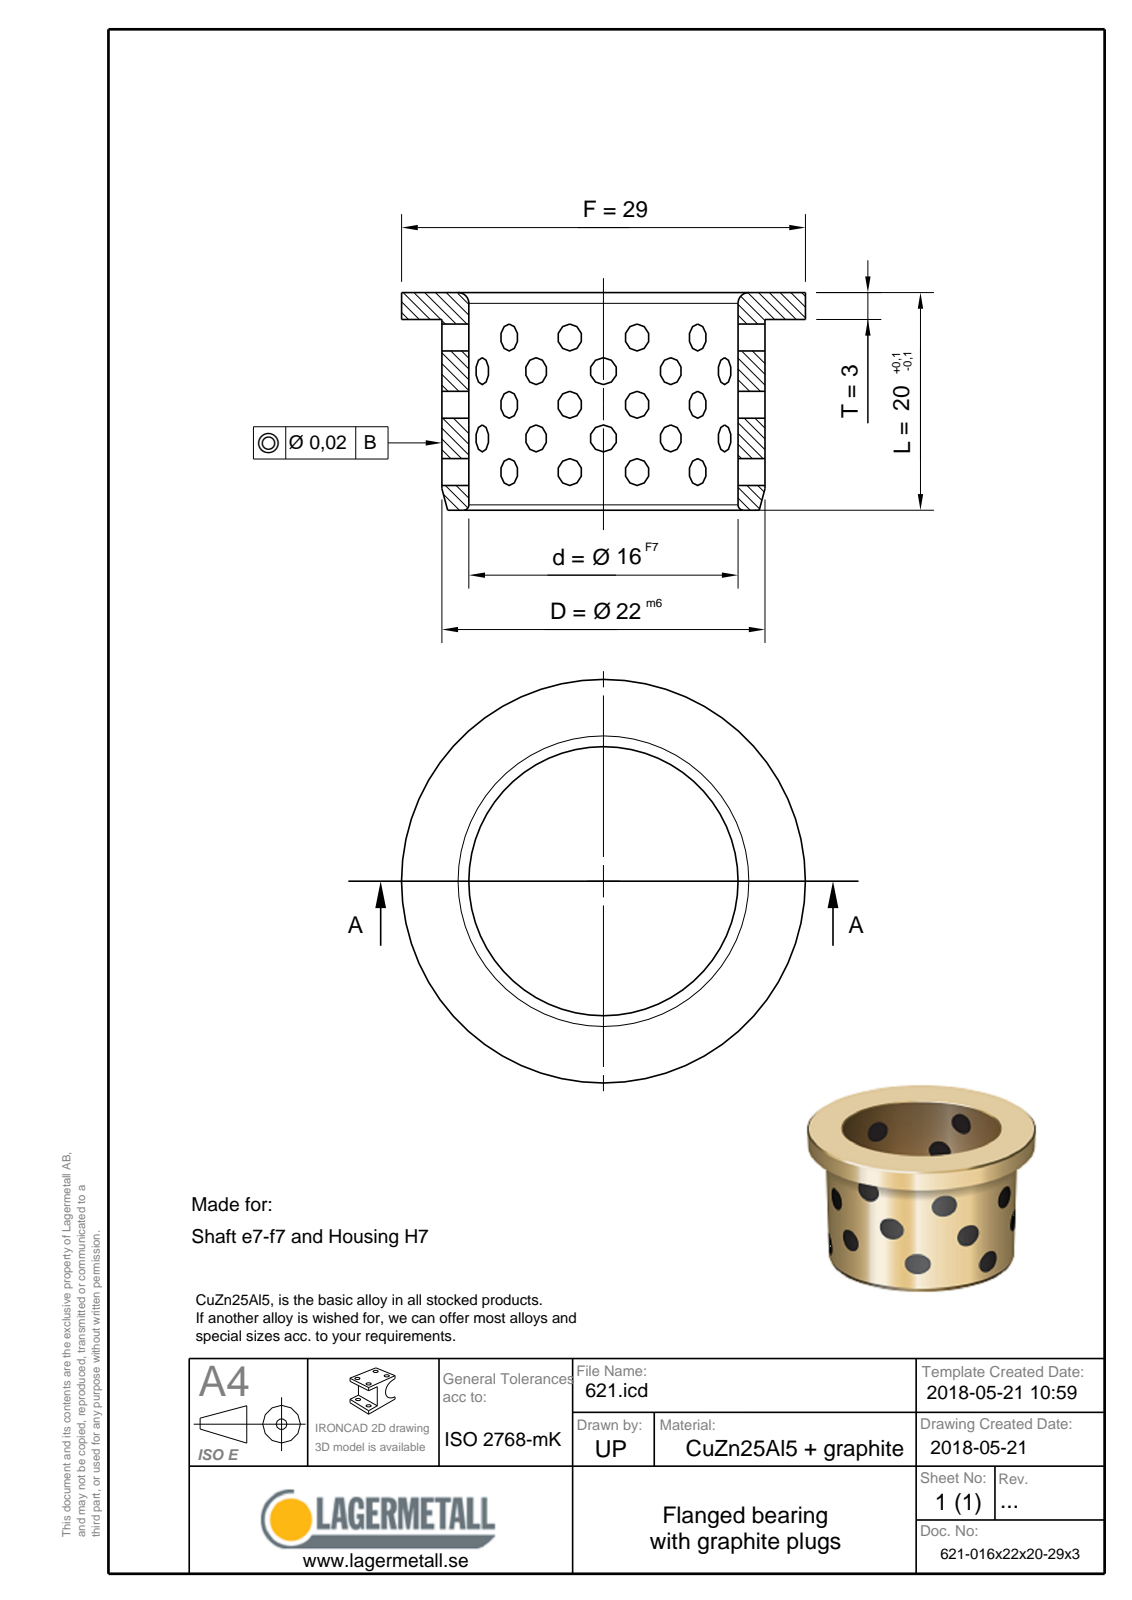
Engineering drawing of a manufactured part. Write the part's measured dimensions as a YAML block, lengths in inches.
part_name: "621-016x22x20-29x3"
step_written_by: "Spatial InterOp 3D (CONFIG_CONTROL_DESIGN)"
units: inches
bodies: {solids: 1, faces: 9, planar: 3, cylindrical: 3, other: 3}
overall_size: [1.142, 1.142, 0.787]
volume: 0.264
surface_area: 5.061
round_holes:
  - {diameter: 0.63, count: 1}
round_bosses_or_shafts:
  - {diameter: 1.142, count: 1}
  - {diameter: 0.866, count: 1}
face_to_face_distances: [0.118, 0.669, 0.787]
